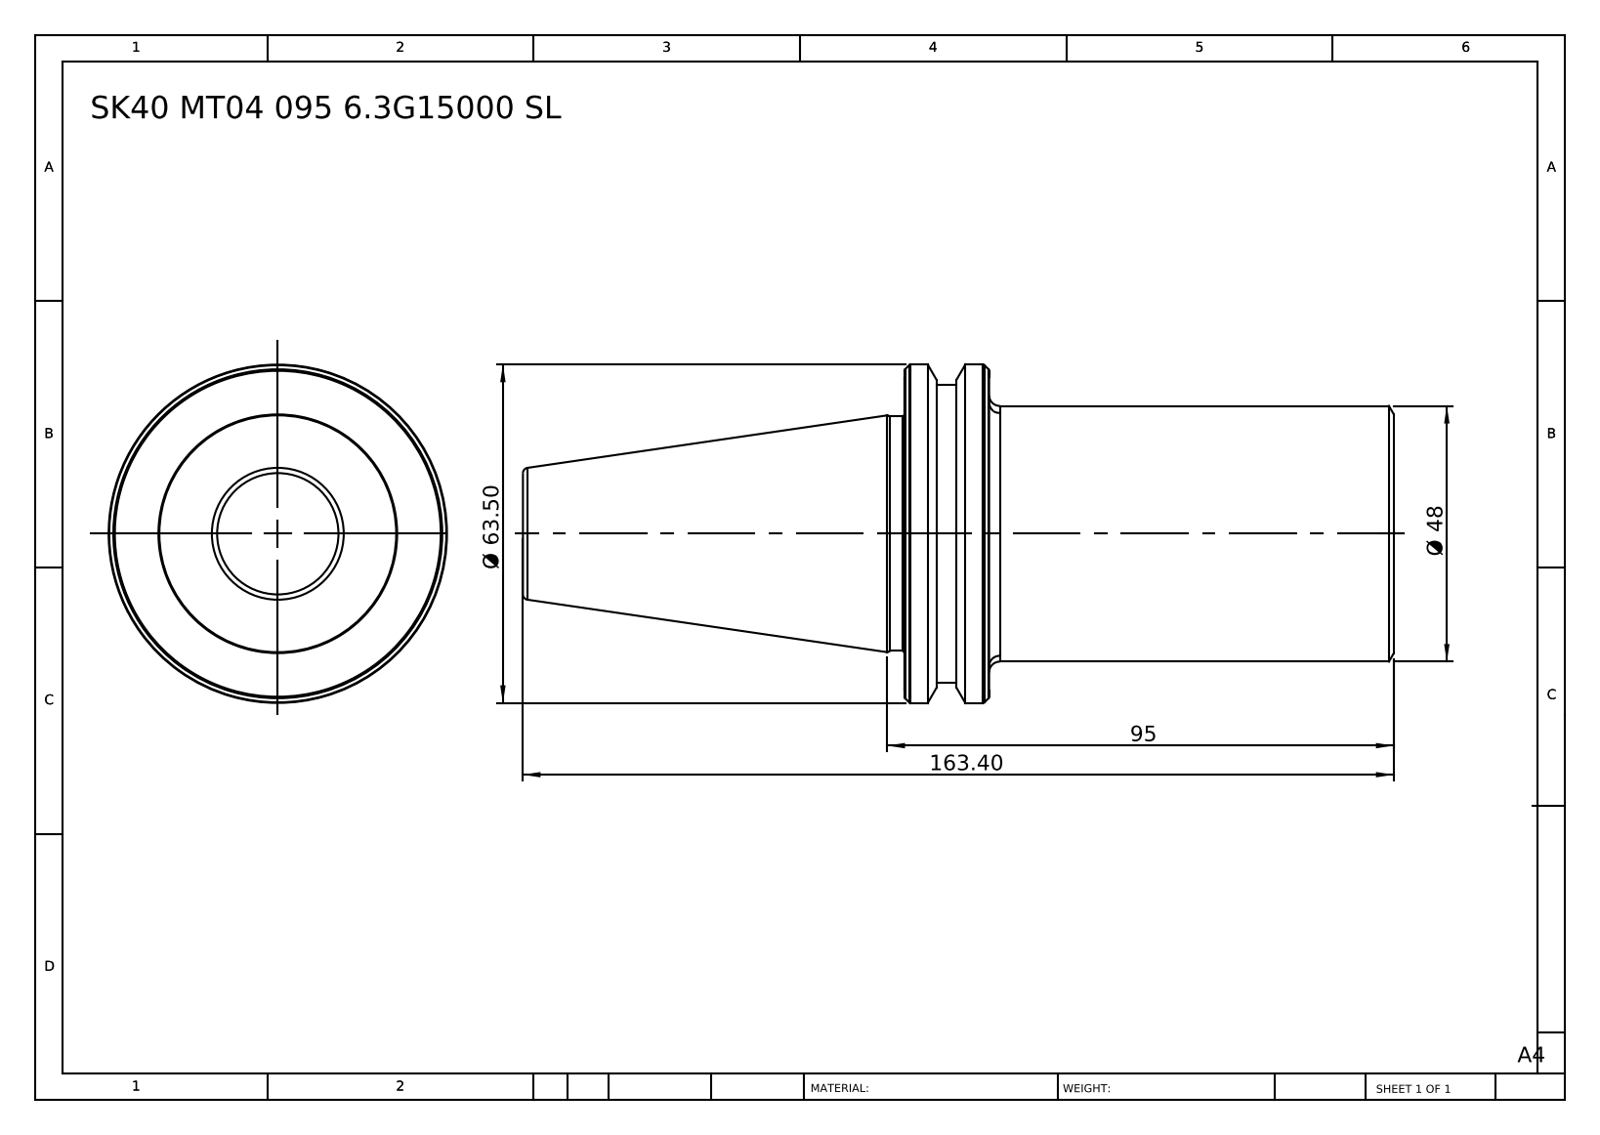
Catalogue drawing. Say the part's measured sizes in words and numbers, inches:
The part is named "SK 40 MT04 095 6.3G15000 SL". Its 3-D file was written by "SolidWorks 2014 (CONFIG_CONTROL_DESIGN)". It is 1 solid with 67 faces: 6 planar, 10 cylindrical and 51 other. Overall it measures 6.433 by 2.5 by 2.5 inches. Its volume is 15.53 cubic inches and its surface area 43.64 square inches. Round bosses or shafts: 1 of diameter 2.5, 1 of diameter 2.205, 1 of diameter 1.89, 1 of diameter 1.732. The main face-to-face distances are 3.614, 2.988, 0.626, 6.433, 3.445, 2.819, 3.378, 0.39, 0.236, 3.055.
